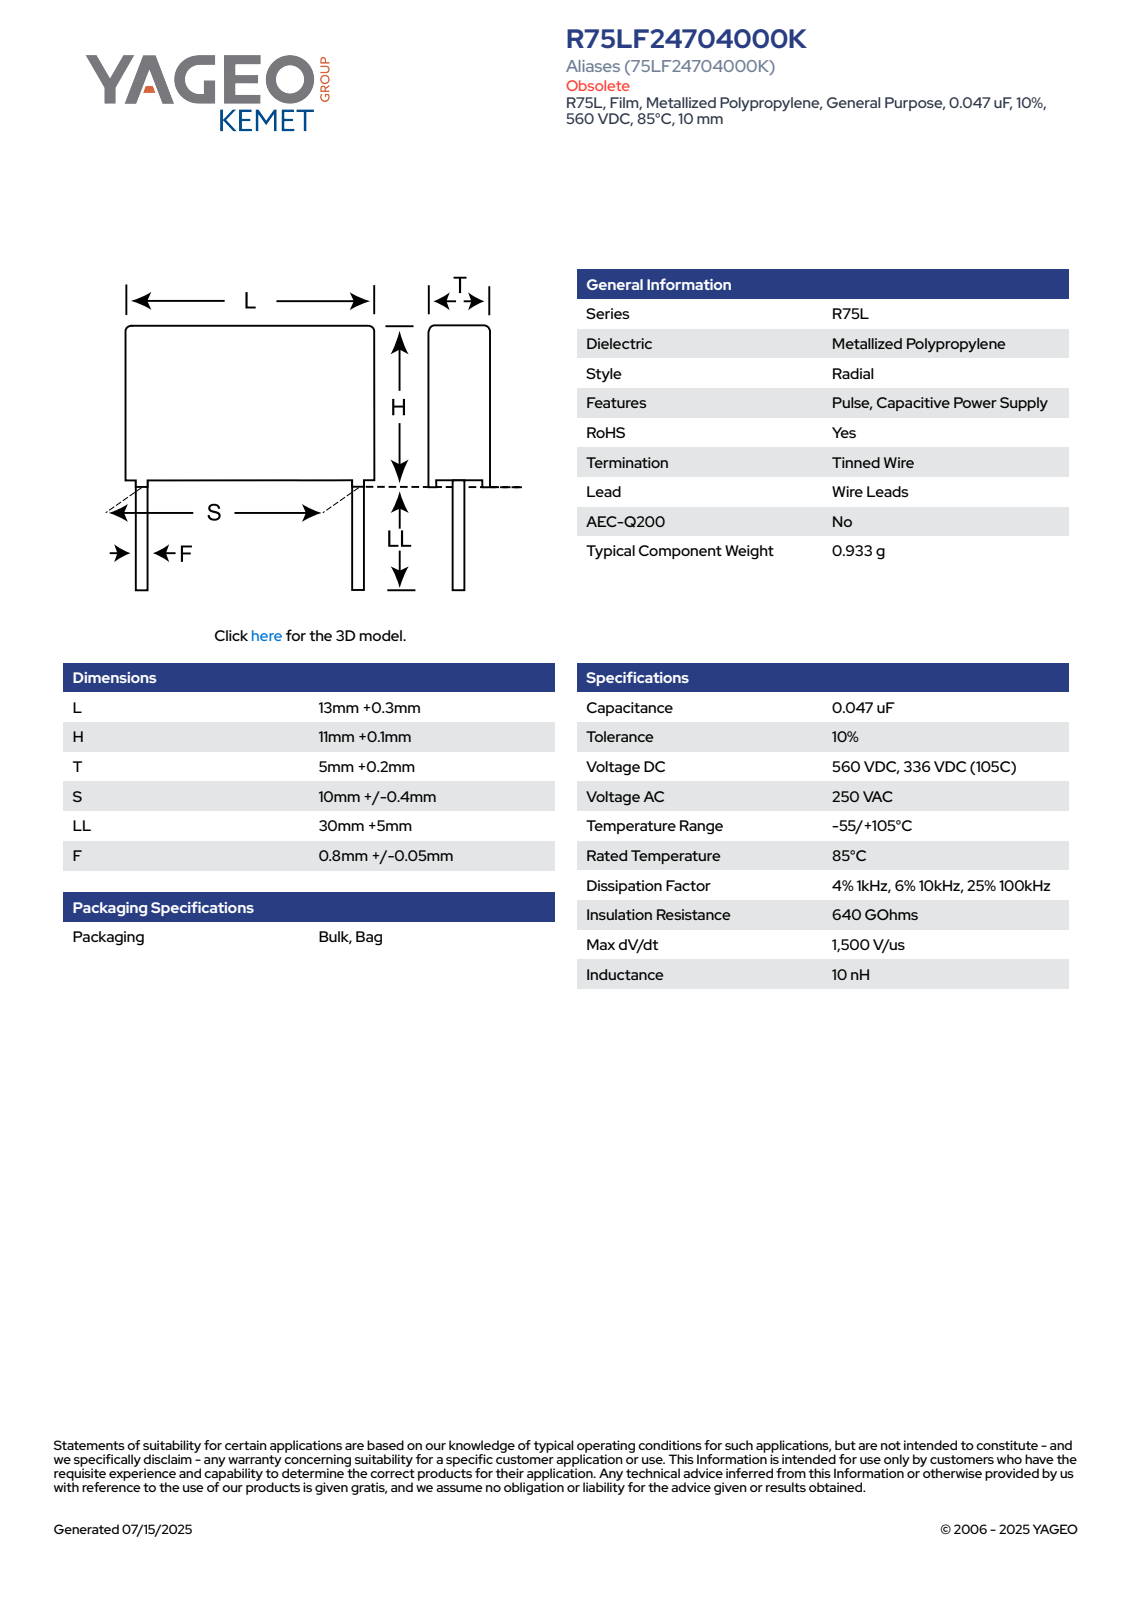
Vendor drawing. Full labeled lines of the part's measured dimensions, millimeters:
Part name (STEP PRODUCT): CFR_RB3_13X11X5_L13.3H11.1T5.2S10LL35F0.85
STEP written by: SolidWorks 2014 (AUTOMOTIVE_DESIGN)
Units: millimetres
Bodies: 4 solids, 85 faces (77 planar, 8 cylindrical, 0 other)
Overall size (bounding box): 46.1 × 13.3 × 5.21
Volume: 764 mm³ · Surface area: 760 mm²
Round bosses / shafts (diameter × count): ⌀0.85 ×2
Partial cylindrical surfaces — rounded edges, fillets, slot ends (radius × count): R0.5 ×4
Main face-to-face distances: 5.2, 13.3, 10.35, 0.44, 4.76, 0.75, 11.1, 4.32, 12.86, 0.37
